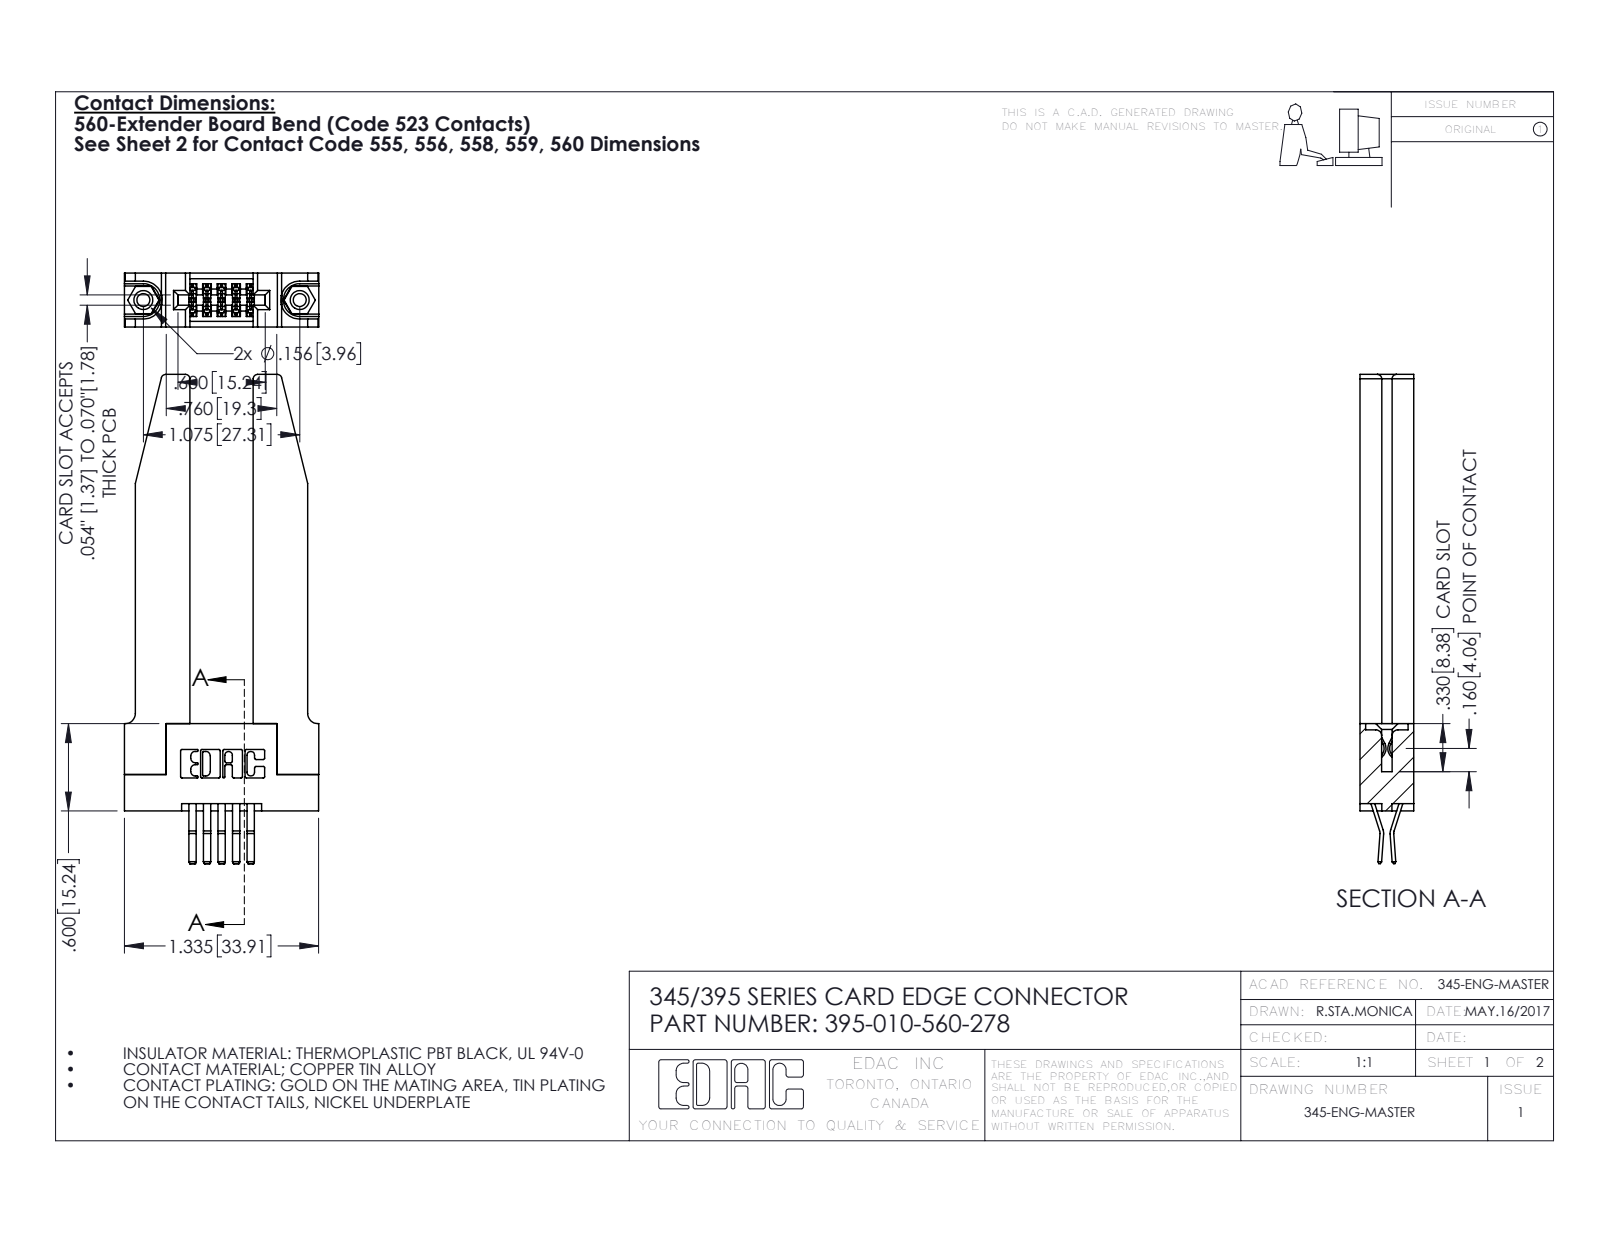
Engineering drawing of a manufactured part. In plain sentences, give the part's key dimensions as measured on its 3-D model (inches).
The part is named "395-010-560-278; 345 Part_Flush Mounting Lugs - 0.156 Dia-TH; 345-220-078_345-220-078; 345-250-001_345-250-001-102 (+1 more)". Its 3-D file was written by "SolidWorks 2016 (CONFIG_CONTROL_DESIGN)". It is 15 solids with 880 faces: 552 planar, 276 cylindrical and 52 other. Overall it measures 3.362 by 1.336 by 0.37 inches. Its volume is 0.658 cubic inches and its surface area 16.67 square inches. Round holes: 2 of diameter 0.089, 2 of diameter 0.125, 2 of diameter 0.156, 1 of diameter 0.064. Round bosses or shafts: 2 of diameter 0.155. Partial cylindrical surfaces (rounded edges, fillets, slot ends): 22 of radius 0.01, 15 of radius 0.006, 8 of radius 0.03, 6 of radius 0.007, 6 of radius 0.031, 3 of radius 0.026, 2 of radius 0.01, 2 of radius 0.014. The main face-to-face distances are 0.37, 0.15, 0.22, 0.435, 0.148, 0.072, 0.077, 0.298, 0.2, 0.025. The hole center spacings are 0.27, 0.847, 1.075.
